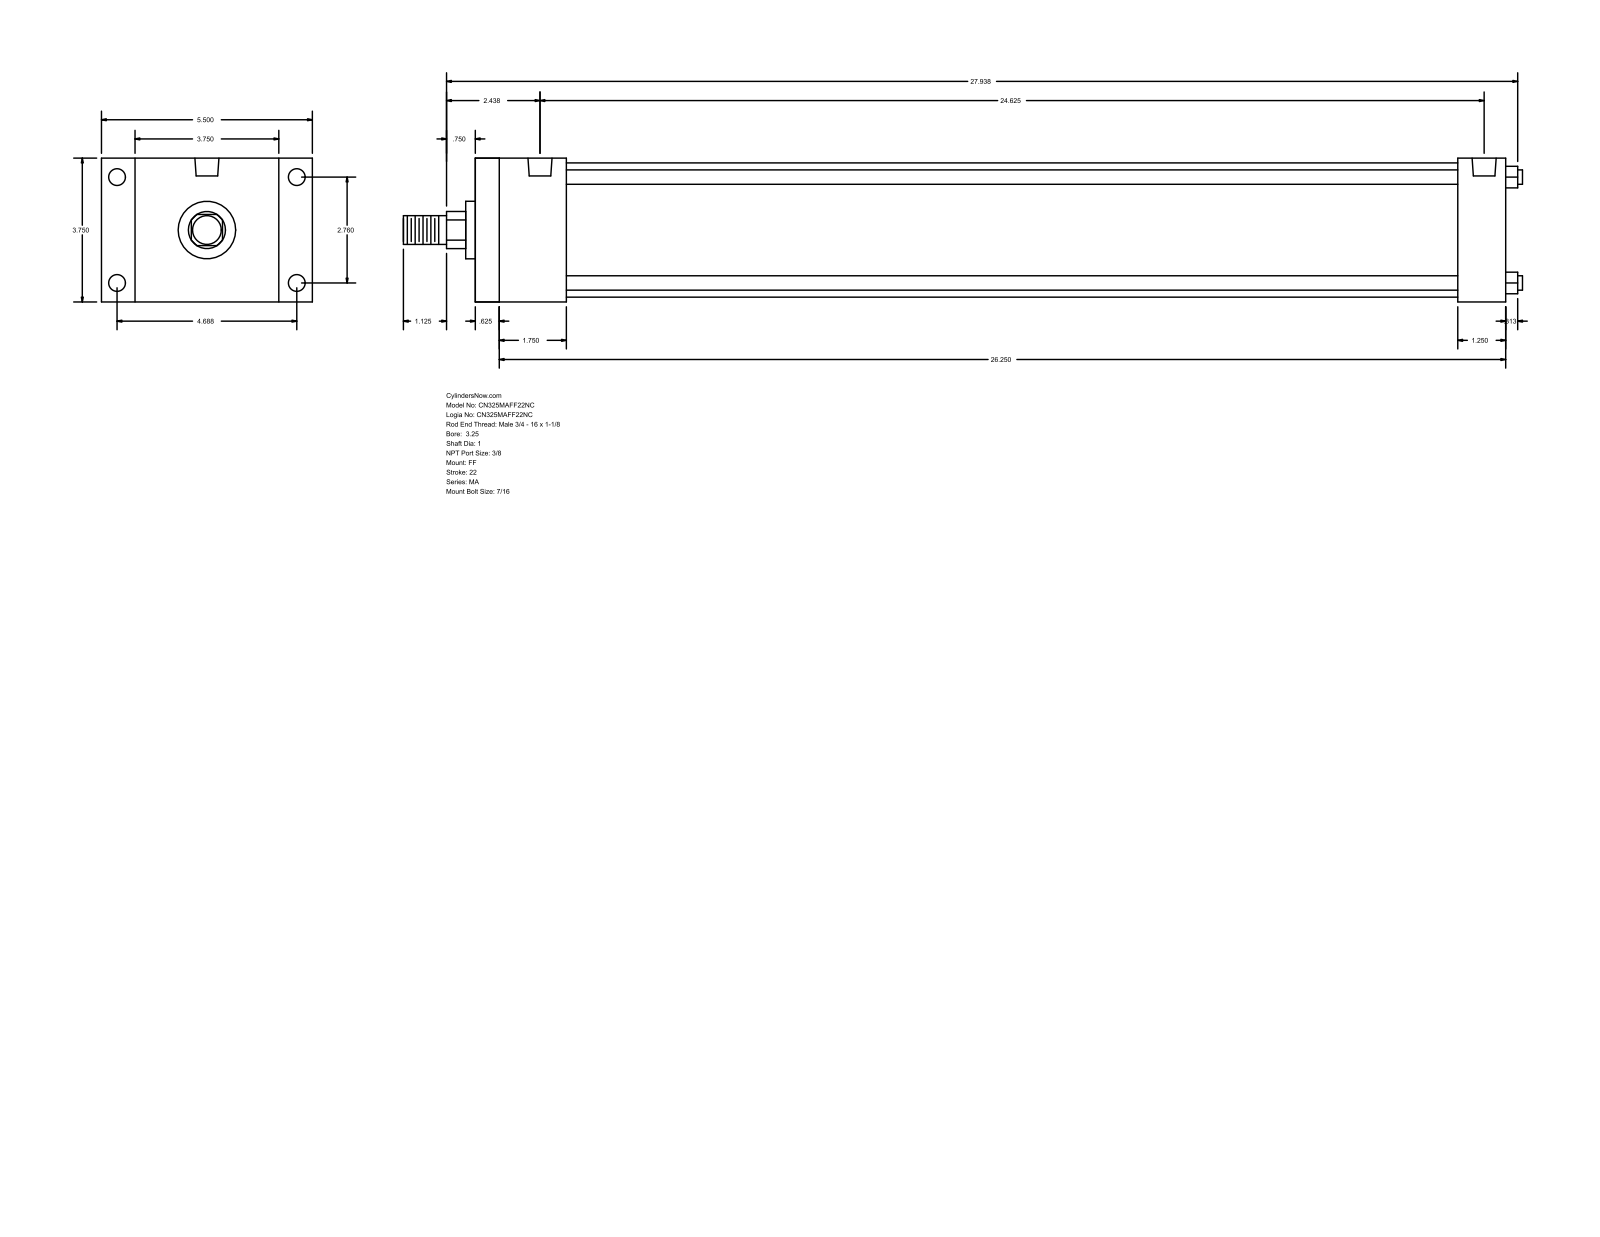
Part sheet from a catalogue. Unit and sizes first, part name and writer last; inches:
Units: inches
Overall size (bounding box): 29.187 × 5.5 × 3.75
Round holes (diameter × count): ⌀0.437 ×8, ⌀0.627 ×2
Round bosses / shafts (diameter × count): ⌀0.375 ×4, ⌀3.5 ×1, ⌀1.5 ×1, ⌀1 ×1, ⌀0.75 ×1
Partial cylindrical surfaces — rounded edges, fillets, slot ends (radius × count): R0.484 ×1
Main face-to-face distances: 3.75, 26.875, 0.625, 26.25, 0.875, 4.625, 2.375, 25.625, 1.75, 25
Hole centre spacings: 2.76, 4.687, 5.439, 24.25, 0.187, 0.188, 24.437, 24.438
Bodies: 0 solids, 92 faces (64 planar, 28 cylindrical, 0 other)
Part name (STEP PRODUCT): MA_FF__0325_1
STEP written by: GSSL Pune (CONFIG_CONTROL_DESIGN)
